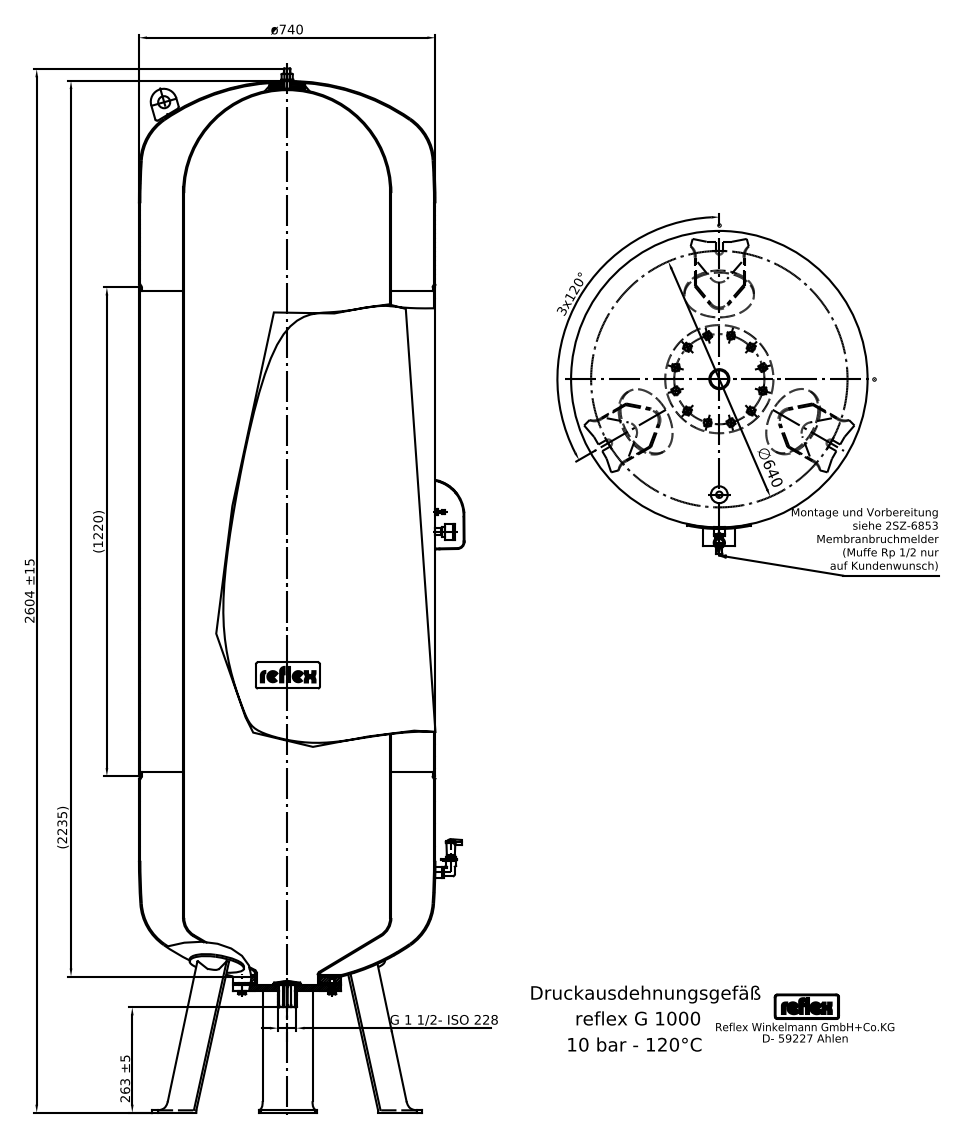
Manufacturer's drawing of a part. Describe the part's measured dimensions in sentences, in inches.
Its 3-D file was written by "Mechanical Desktop 2008 (CONFIG_CONTROL_DESIGN)". It is 22 solids with 480 faces: 242 planar, 150 cylindrical and 88 other. Overall it measures 102.52 by 31.969 by 29.179 inches. Its volume is 55 890 cubic inches and its surface area 12 790 square inches. Round holes: 1 of diameter 0.394, 1 of diameter 6.299. Round bosses or shafts: 13 of diameter 0.63, 3 of diameter 0.787, 2 of diameter 1.102, 2 of diameter 1.024, 2 of diameter 0.945, 1 of diameter 29.134, 1 of diameter 10.63, 1 of diameter 1.902. Partial cylindrical surfaces (rounded edges, fillets, slot ends): 18 of radius 0.984, 4 of radius 0.155, 3 of radius 0.062, 3 of radius 0.354, 2 of radius 0.106, 2 of radius 0.186, 2 of radius 0.256, 2 of radius 0.259. The main face-to-face distances are 73.701, 0.63, 0.827, 7.677, 81.378, 0.235, 0.232, 8.307, 82.008, 0.197. The hole center spacings are 15.177.
